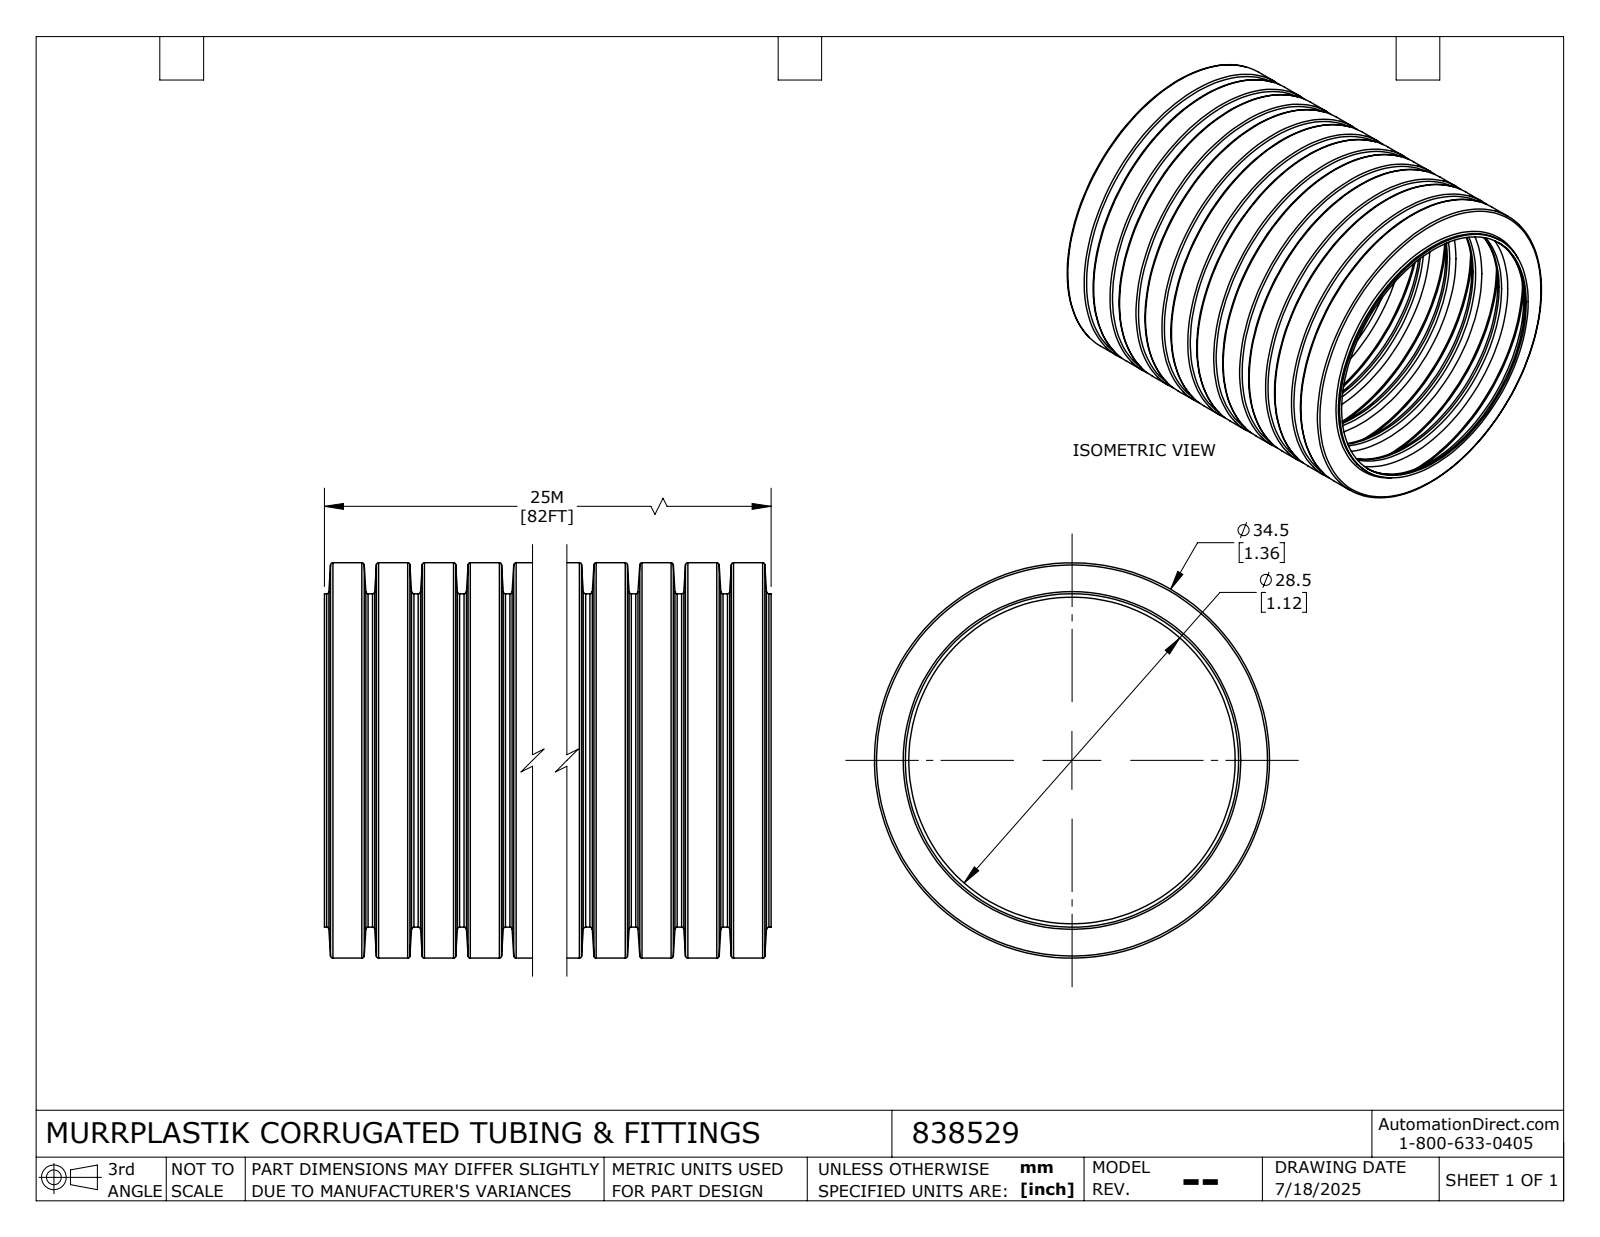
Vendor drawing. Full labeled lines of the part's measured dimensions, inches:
Part name (STEP PRODUCT): 838529_Default
STEP written by: SolidWorks 2024 (CONFIG_CONTROL_DESIGN)
Units: inches
Bodies: 1 solid, 164 faces (2 planar, 42 cylindrical, 120 other)
Overall size (bounding box): 1.575 × 1.358 × 1.358
Volume: 0.161 in³ · Surface area: 27.27 in²
Round holes (diameter × count): ⌀1.122 ×1, ⌀1.335 ×1
Round bosses / shafts (diameter × count): ⌀1.358 ×1, ⌀1.146 ×1
Main face-to-face distances: 1.575
